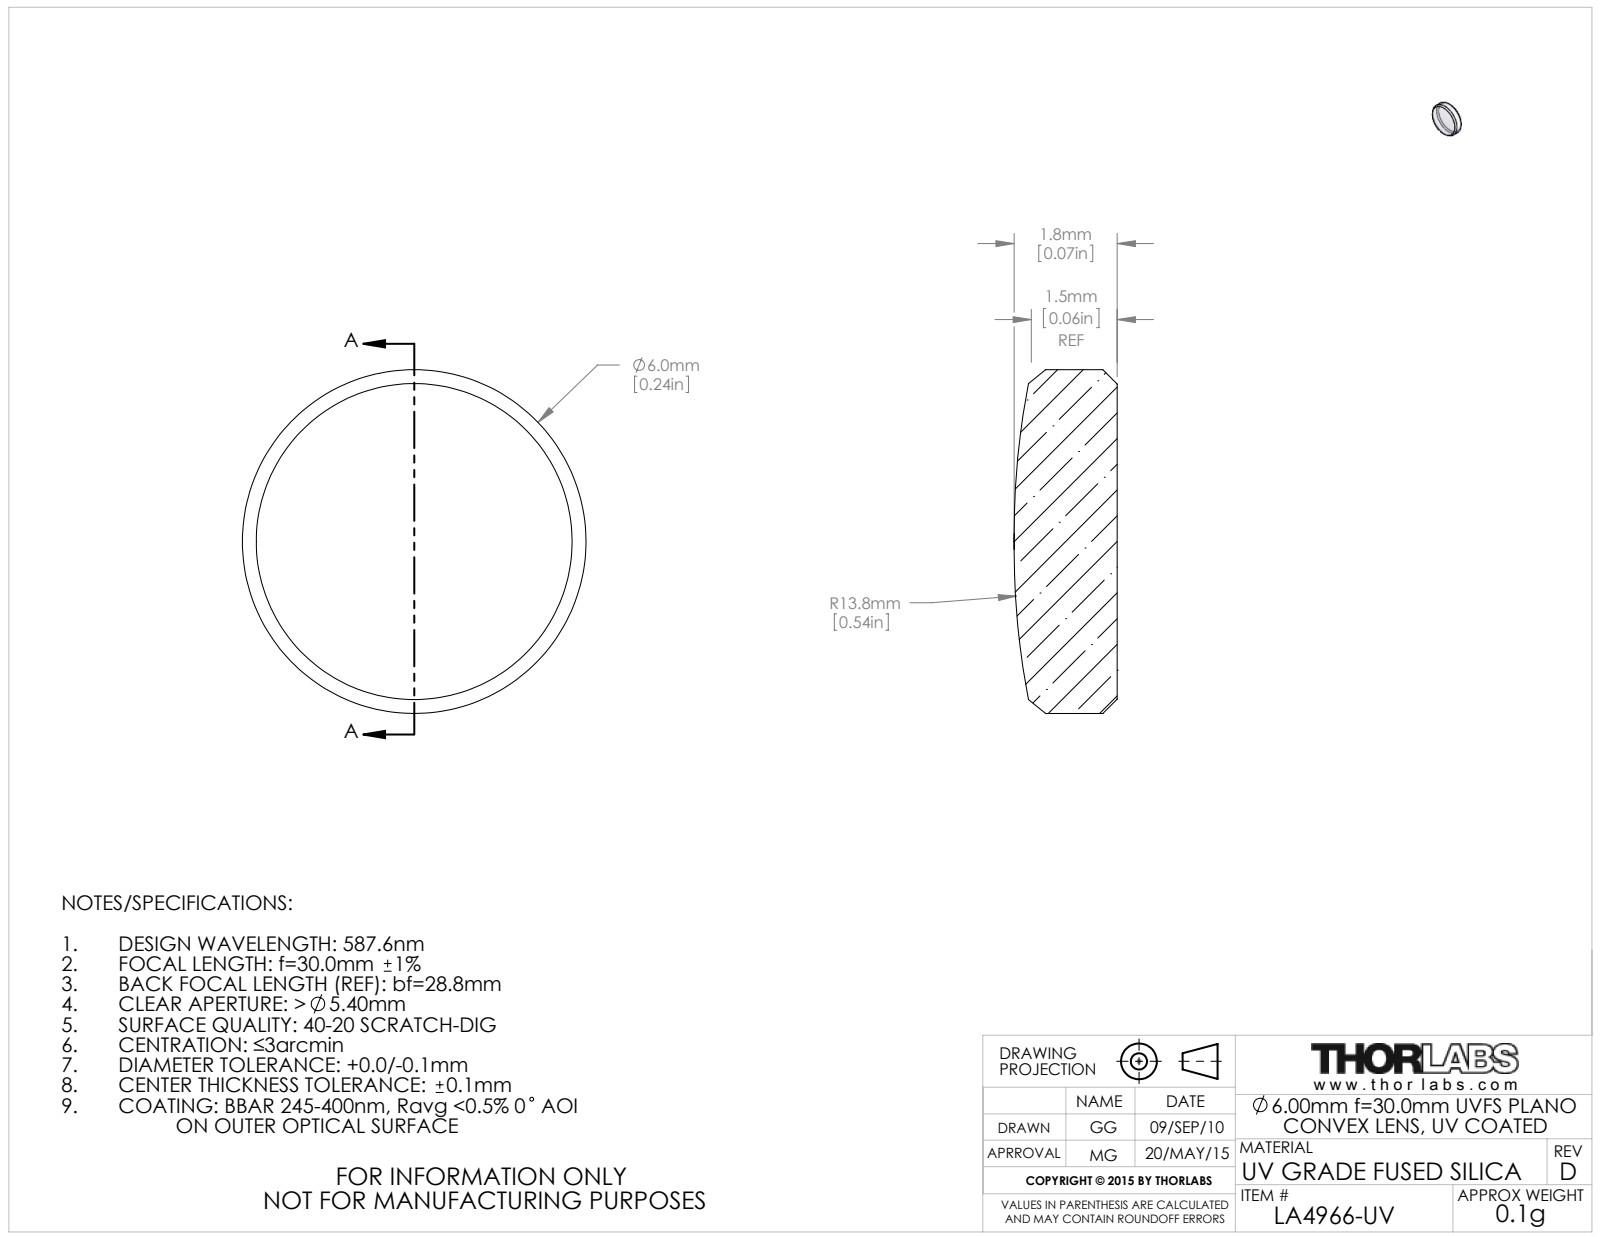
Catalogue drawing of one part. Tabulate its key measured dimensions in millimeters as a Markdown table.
| quantity | value |
| --- | --- |
| part name | 4271-E0W |
| STEP written by | SolidWorks 2014 (CONFIG_CONTROL_DESIGN) |
| units | millimeters |
| bodies | 1 solid, 9 faces (1 planar, 2 cylindrical, 6 other) |
| overall size | 6 × 6 × 1.8 |
| volume | 46 mm³ |
| surface area | 80 mm² |
| round bosses / shafts (diameter × count) | 6 × 1 |
